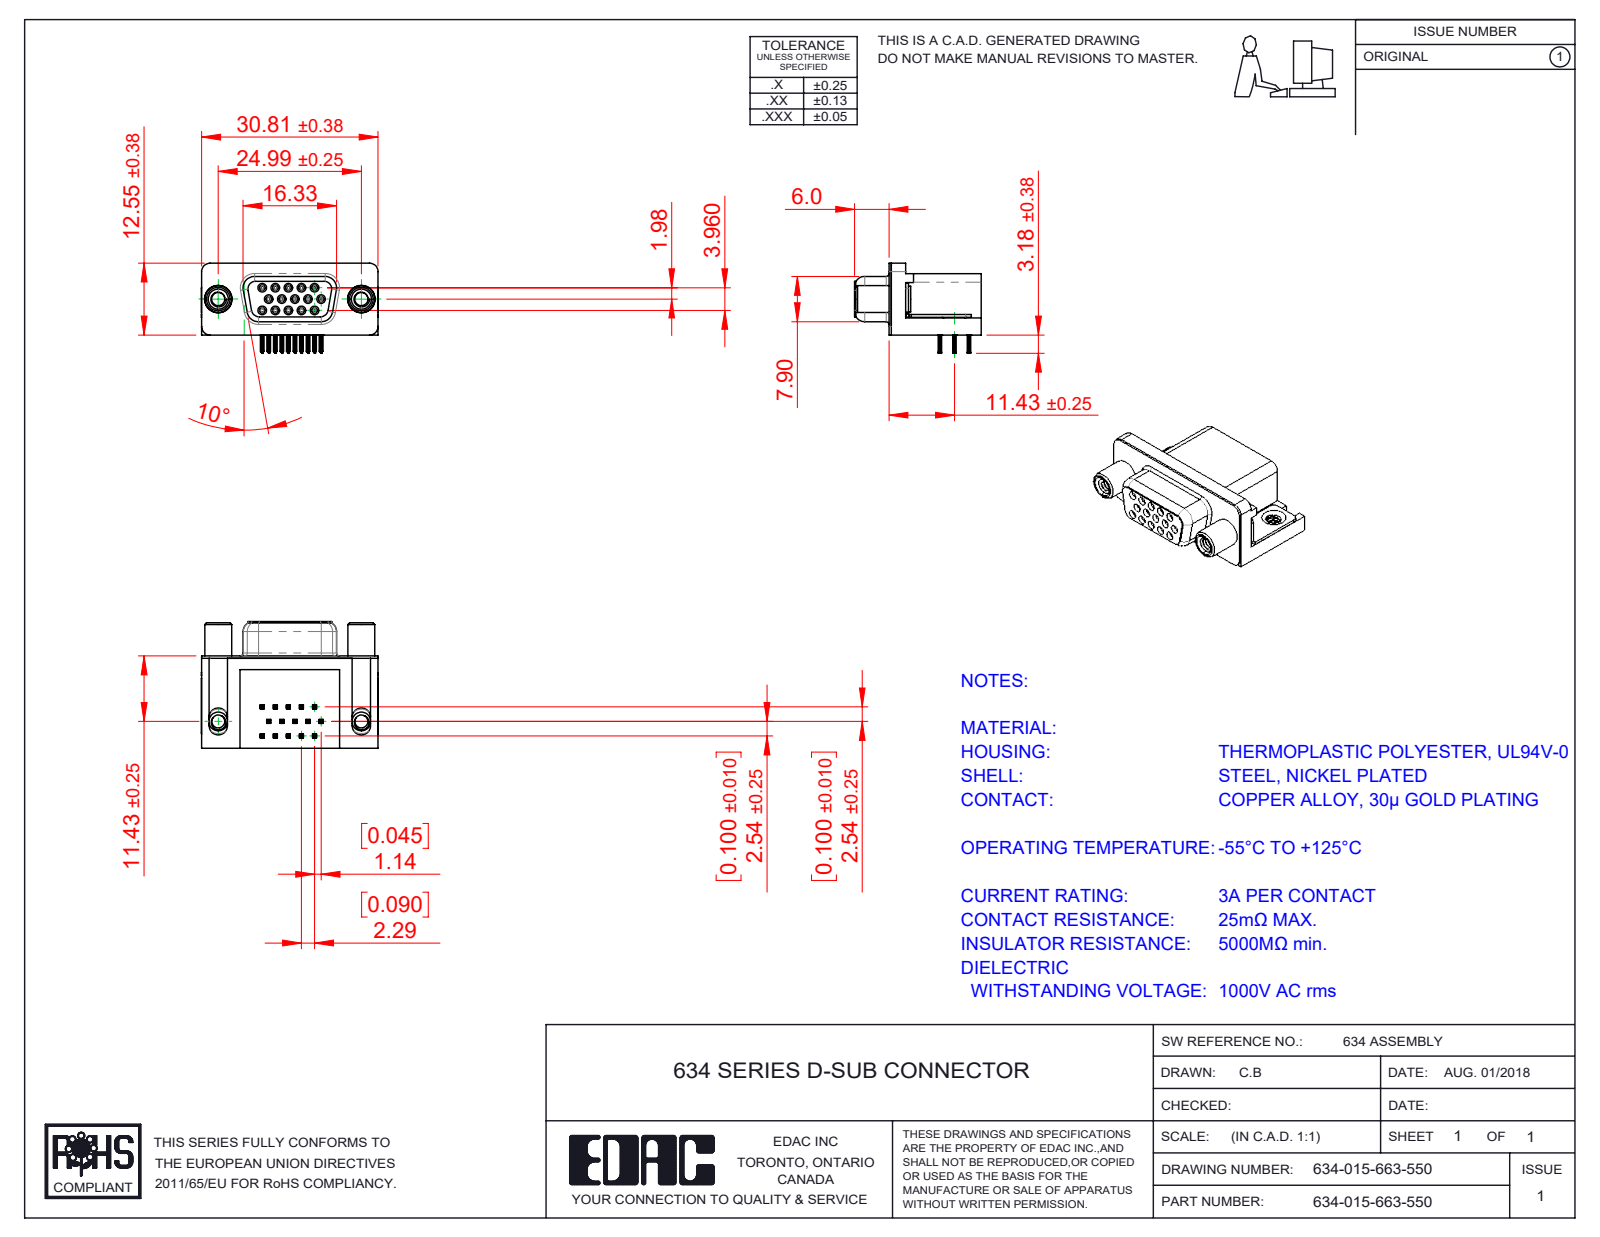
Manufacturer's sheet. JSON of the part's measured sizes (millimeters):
{"part_name": "Contact Top; Round Threaded Standoff; Contact Middle; Contact Bottom (+4 more)", "step_written_by": "SolidWorks 2016 (CONFIG_CONTROL_DESIGN)", "units": "millimeters", "bodies": {"solids": 21, "faces": 2535, "planar": 1100, "cylindrical": 613, "other": 822}, "overall_size": [30.89, 22.1, 16.25], "volume_mm3": 4653, "surface_area_mm2": 6775, "round_holes": [[0.8, 15], [0.9, 15], [2, 2], [2.3, 2], [3.1, 2], [4, 2], [4.8, 2], [5, 2]], "round_bosses_or_shafts": [[1.2, 15], [4.9, 2], [4.7, 2], [4.5, 2], [3.85, 2], [3, 2]], "partial_cylinders_radius": [[0.1, 120], [0.15, 60], [0.35, 30], [1, 19], [0.34, 15], [1.35, 8], [1.6, 8], [1.5, 7]], "face_to_face_distances": [0.4, 10.35, 15.7, 16.1, 0.35, 2.5, 2.9, 0.6, 10.7, 6.7], "hole_center_spacings": [2.29, 2.28, 3.96, 4.57, 6.05, 3.97, 4.58, 6.86]}
